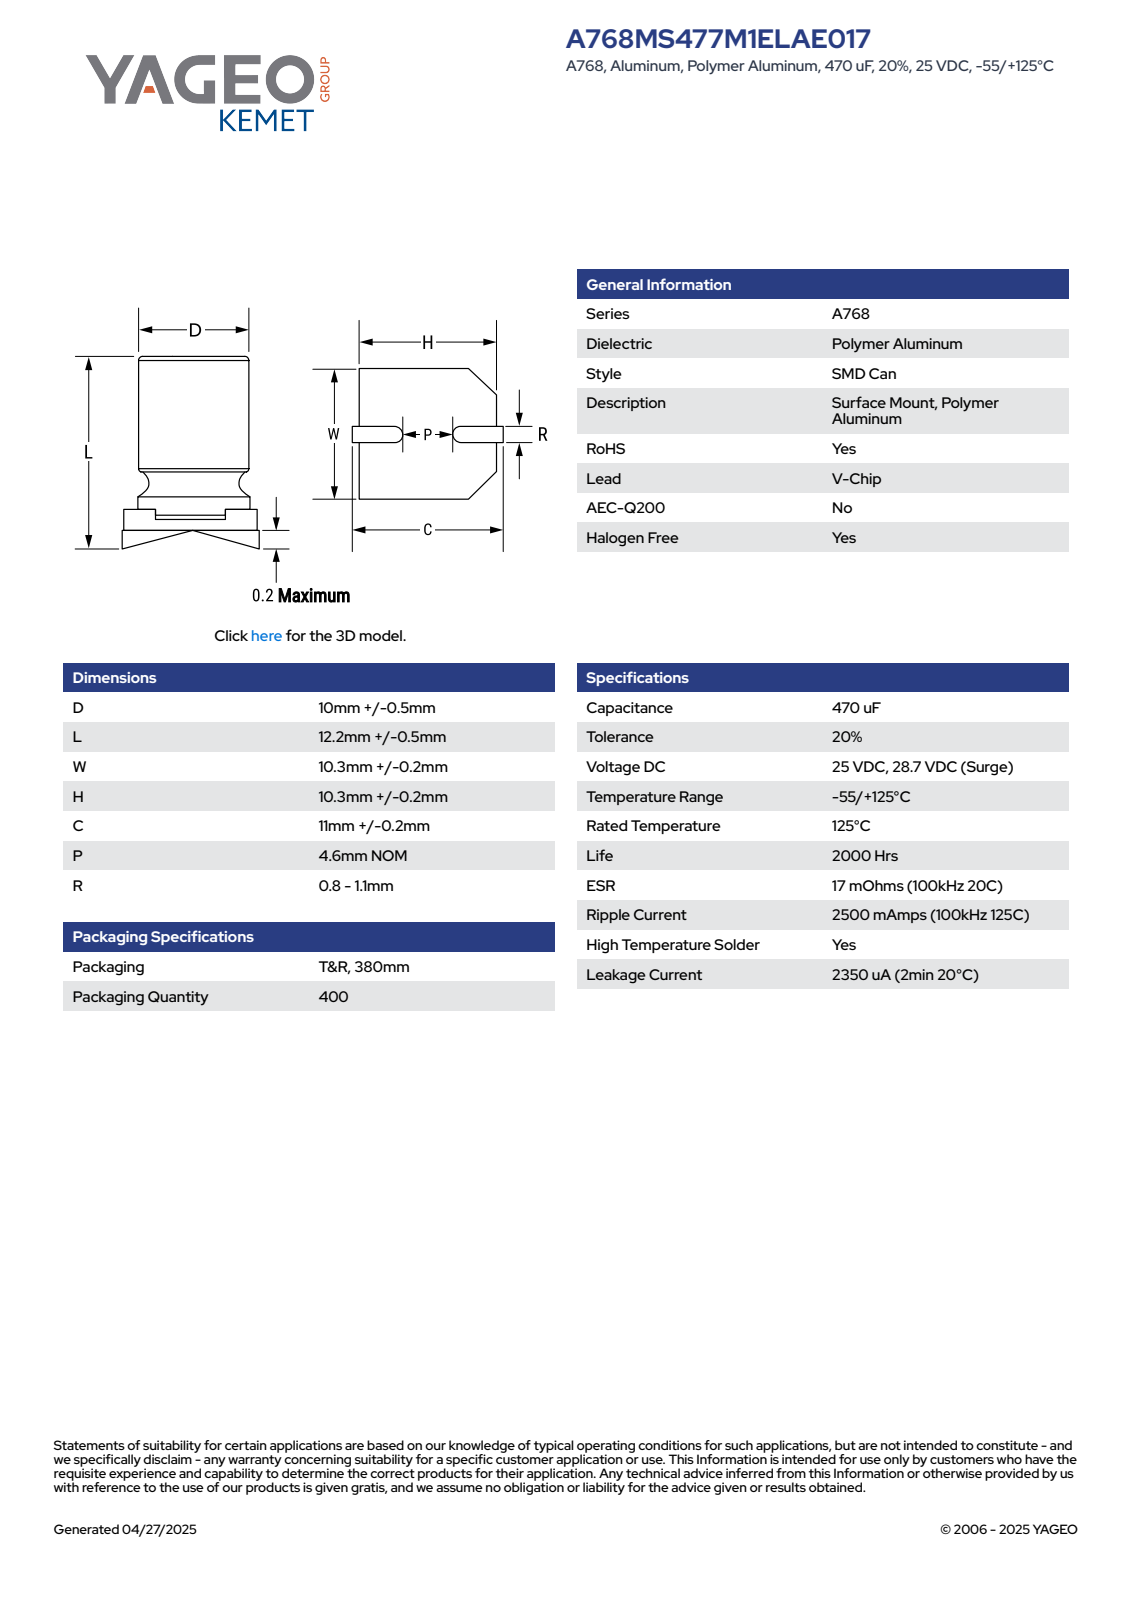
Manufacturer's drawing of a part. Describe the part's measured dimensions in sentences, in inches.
The part is named "CAC_KSA_10X12.2_D10.5L12.7H10.5C11.2P4.6W10.5R1.1". Its 3-D file was written by "SolidWorks 2020 (AUTOMOTIVE_DESIGN)". It is 5 solids with 76 faces: 59 planar, 11 cylindrical and 6 other. Overall it measures 0.5 by 0.441 by 0.413 inches. Its volume is 0.063 cubic inches and its surface area 1.37 square inches. Round bosses or shafts: 1 of diameter 0.395. Partial cylindrical surfaces (rounded edges, fillets, slot ends): 2 of radius 0.008, 1 of radius 0.164, 1 of radius 0.207. The main face-to-face distances are 0.025, 0.492, 0.467, 0.493, 0.468, 0.413, 0.125, 0.1, 0.367, 0.368.
